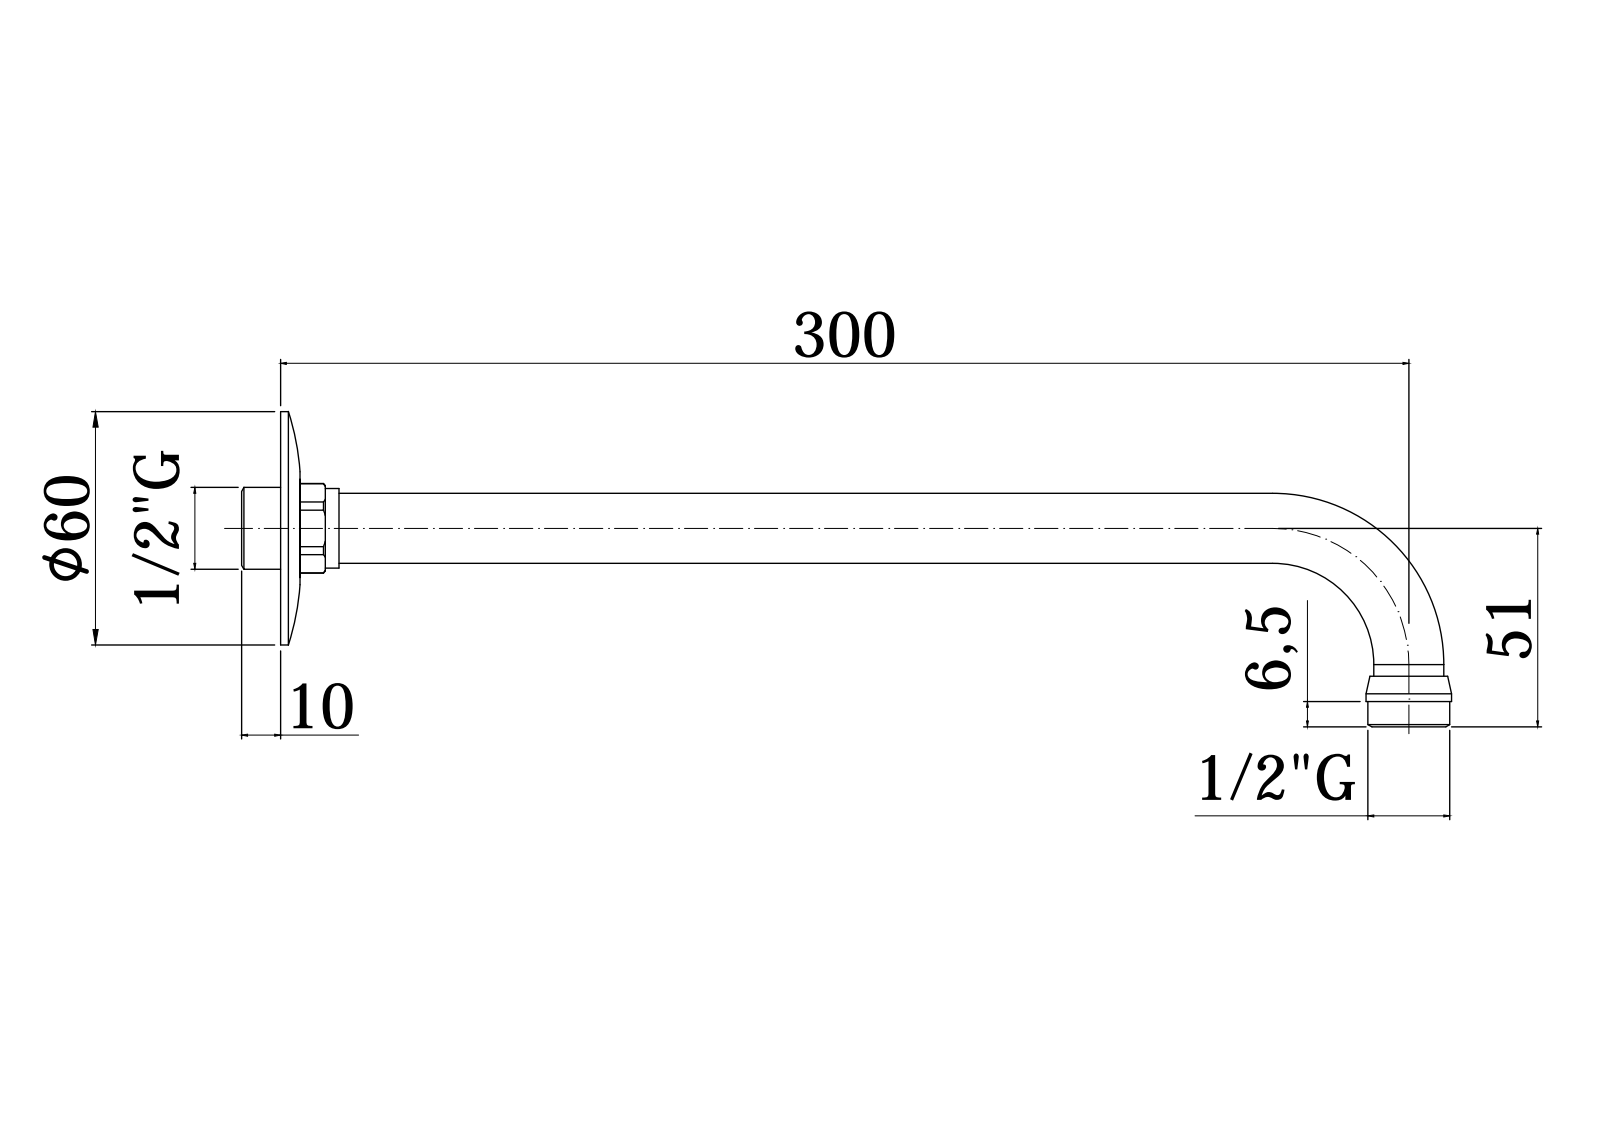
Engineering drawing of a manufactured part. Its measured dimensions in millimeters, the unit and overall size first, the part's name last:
Units: millimetres
Overall size (bounding box): 311 × 80 × 58
Round holes (diameter × count): ⌀15 ×2, ⌀17 ×1, ⌀57 ×1
Round bosses / shafts (diameter × count): ⌀21 ×2, ⌀58 ×1, ⌀22 ×1, ⌀18 ×1
Partial cylindrical surfaces — rounded edges, fillets, slot ends (radius × count): R11.5 ×1
Main face-to-face distances: 4, 21, 4.5, 0.5, 15, 11, 10.5, 13, 8, 3.5
Volume: 14 901 mm³ · Surface area: 43 479 mm²
Bodies: 1 solid, 88 faces (24 planar, 26 cylindrical, 38 other)
Part name (STEP PRODUCT): ZSOF016CR
STEP written by: CREO PARAMETRIC BY PTC INC, 2020044 (CONFIG_CONTROL_DESIGN)
